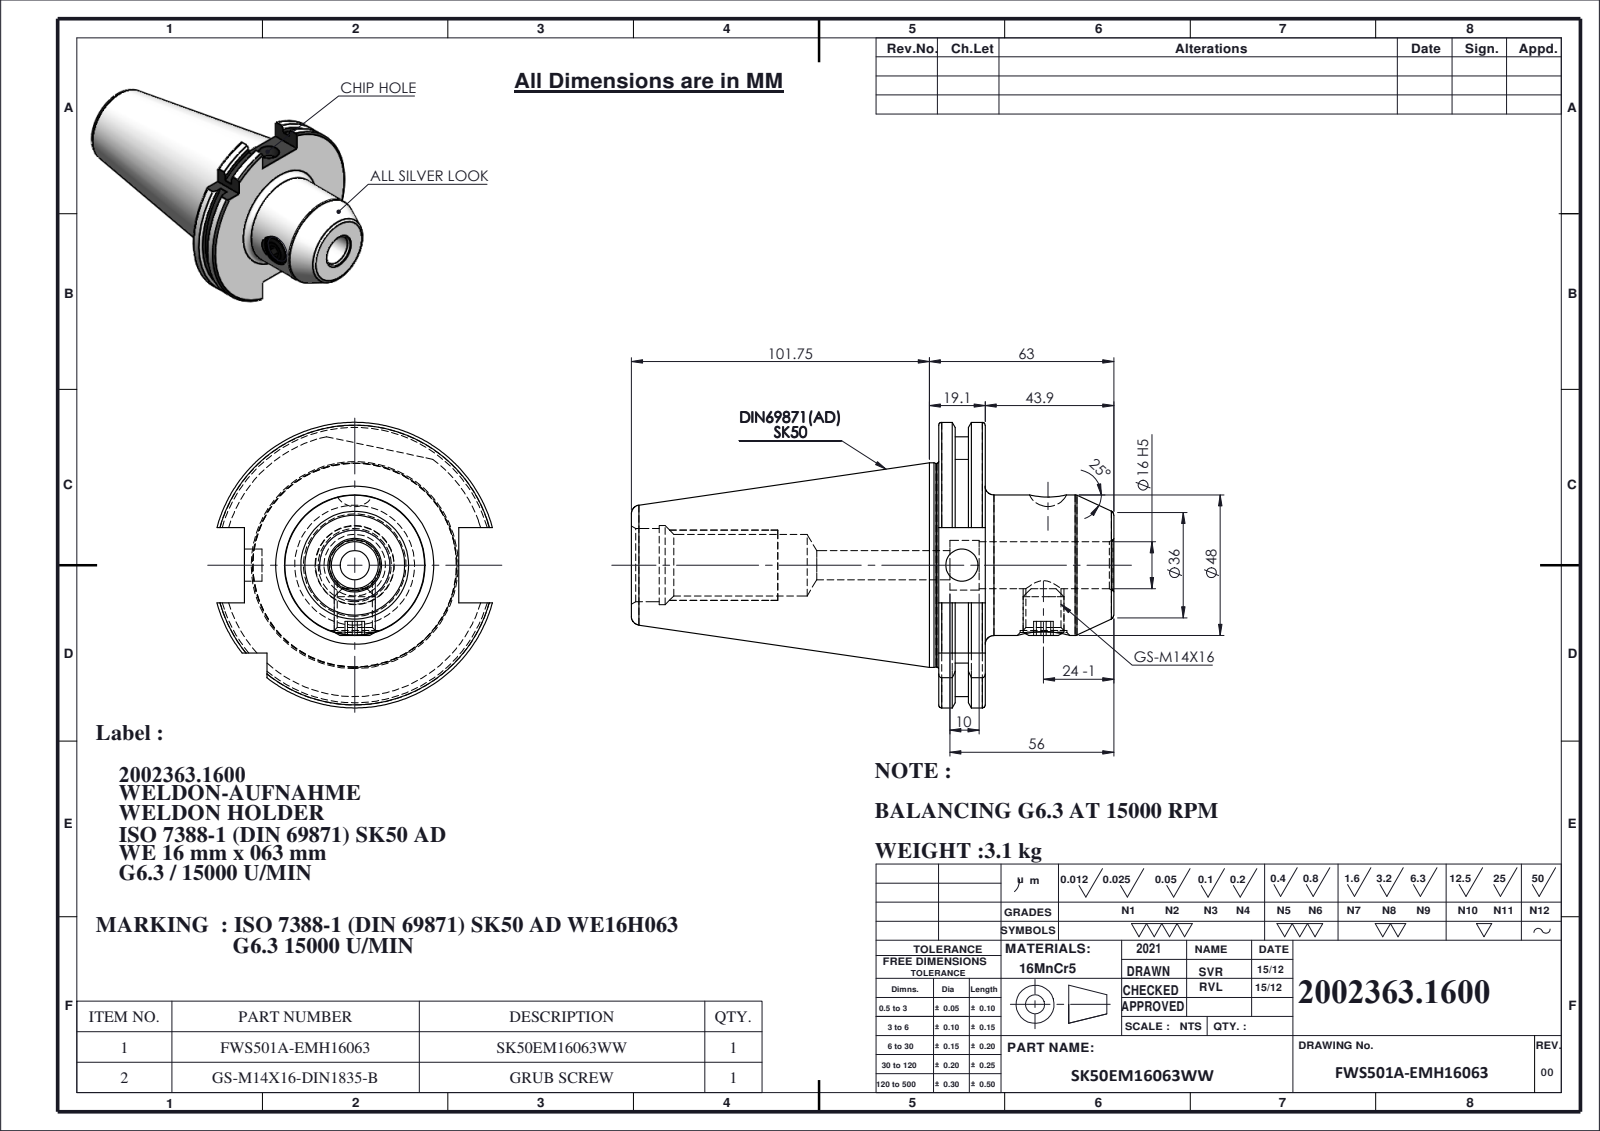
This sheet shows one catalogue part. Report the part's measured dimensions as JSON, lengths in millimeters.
{"part_name": "SK50EM16063WW; 91506-WE116063; GS-M14X16-DIN1835-B_ISO 4026 - M12 x 12-N; GS-M14X16-DIN1835-B", "step_written_by": "SolidWorks 2018 (CONFIG_CONTROL_DESIGN)", "units": "millimeters", "bodies": {"solids": 2, "faces": 127, "planar": 33, "cylindrical": 39, "other": 55}, "overall_size": [164.75, 97.5, 94.05], "volume_mm3": 398327, "surface_area_mm2": 51727, "round_holes": [[16, 2], [10, 1], [11, 1], [12, 1], [17, 1], [21, 1], [25, 1], [27, 1]], "round_bosses_or_shafts": [[69.85, 1], [69.45, 1], [48, 1], [14, 1]], "partial_cylinders_radius": [[44.9, 1], [48.75, 1]], "face_to_face_distances": [15.9, 59.8, 43.9, 5.65, 10.25, 54.15, 10.14, 4.49, 5.76, 49.66]}
